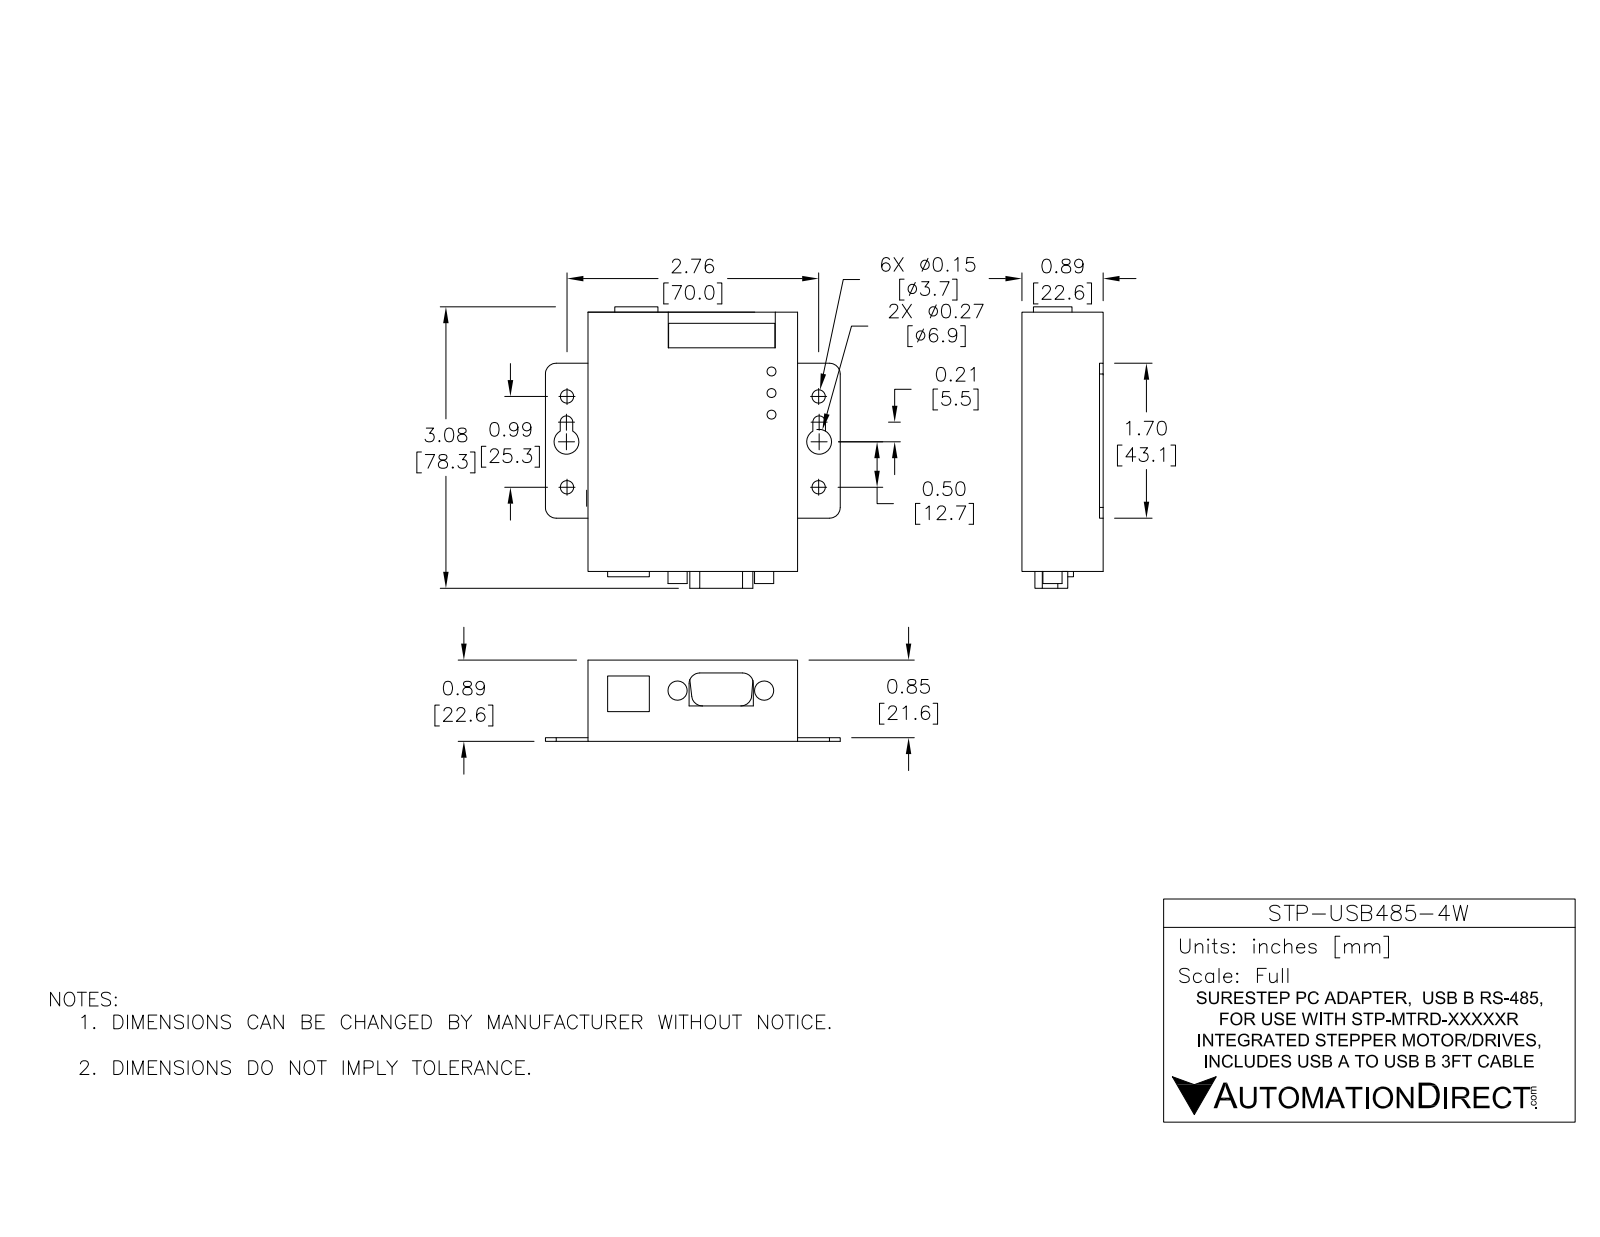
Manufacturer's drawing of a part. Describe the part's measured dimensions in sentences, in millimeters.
The part is named "STP-USB485-4W". Its 3-D file was written by "SolidWorks 2017 (AUTOMOTIVE_DESIGN)". It is 1 solid with 87 faces: 53 planar, 34 cylindrical and 0 other. Overall it measures 82.02 by 78.3 by 22.6 millimeters. Its volume is 95 157 cubic millimeters and its surface area 17 527 square millimeters. Round holes: 4 of diameter 3.7, 3 of diameter 2.5, 2 of diameter 6.9. Round bosses or shafts: 2 of diameter 5.33. Partial cylindrical surfaces (rounded edges, fillets, slot ends): 8 of radius 3, 2 of radius 1.75. The main face-to-face distances are 22.6, 58.3, 1, 21.6, 72.1, 69, 3.1, 14, 8.6, 7.6. The hole center spacings are 6, 12.6, 12.65, 25.25, 70.02, 71.28, 71.29, 74.43.
